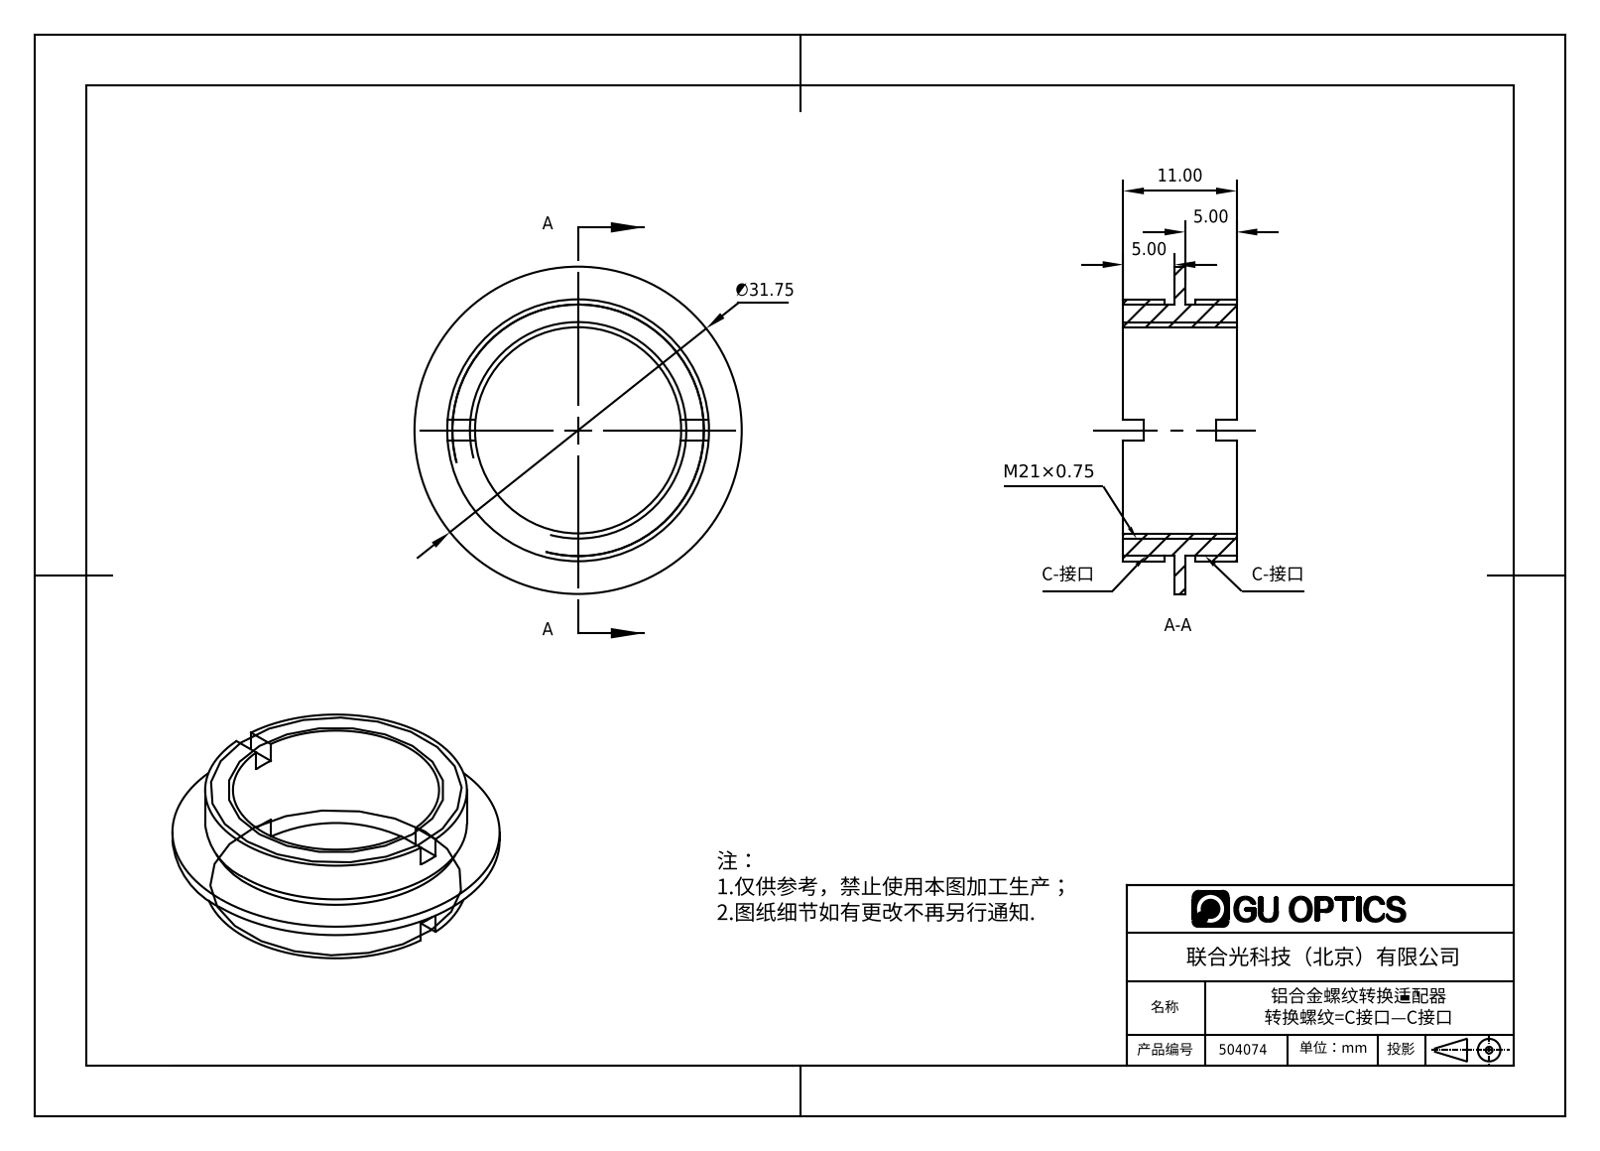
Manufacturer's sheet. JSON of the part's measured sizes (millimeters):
{"part_name": "504074", "step_written_by": "SolidWorks 2016 (AUTOMOTIVE_DESIGN)", "units": "millimeters", "bodies": {"solids": 1, "faces": 32, "planar": 20, "cylindrical": 12, "other": 0}, "overall_size": [31.75, 31.75, 11], "volume_mm3": 2282, "surface_area_mm2": 2706, "round_holes": [[20, 1]], "round_bosses_or_shafts": [[31.75, 1], [25.4, 1], [24.4, 1]], "face_to_face_distances": [1, 5, 6, 11, 2, 4, 7, 3, 9]}
